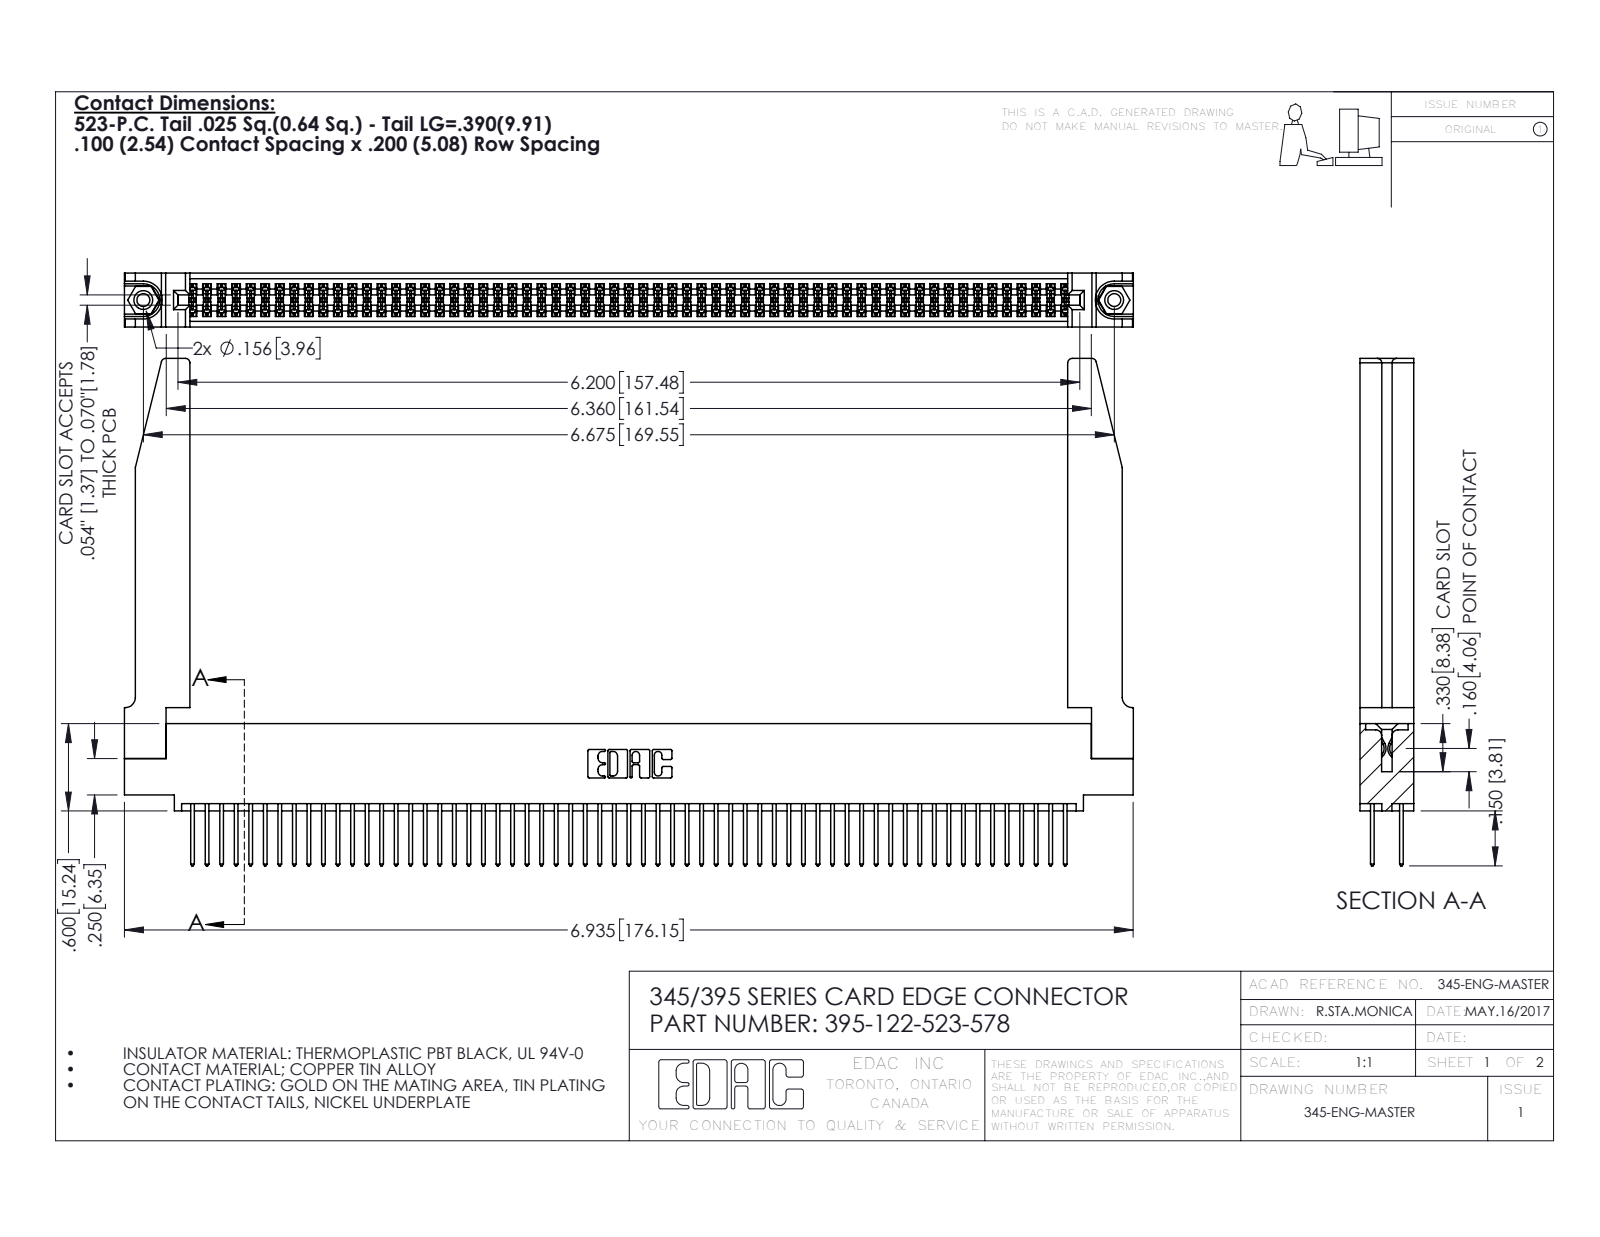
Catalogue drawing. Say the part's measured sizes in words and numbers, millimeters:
The part is named "345-220-078_345-220-078; 395-122-523-578; 345-292-001_345-293-123; 345 Part_0.110 Offset - 0.156 Dia-TH (+1 more)". Its 3-D file was written by "SolidWorks 2016 (CONFIG_CONTROL_DESIGN)". It is 127 solids with 6464 faces: 4252 planar, 2160 cylindrical and 52 other. Overall it measures 176.2 by 88.6 by 9.4 millimeters. Its volume is 25 240 cubic millimeters and its surface area 34 240 square millimeters. Round holes: 2 of diameter 2.3, 2 of diameter 3.2, 2 of diameter 4, 1 of diameter 1.6. Round bosses or shafts: 2 of diameter 3.9. Partial cylindrical surfaces (rounded edges, fillets, slot ends): 183 of radius 0.2, 122 of radius 0.3, 22 of radius 0.3, 8 of radius 0.8, 6 of radius 0.2, 6 of radius 0.8, 3 of radius 0.7, 2 of radius 0.4. The main face-to-face distances are 1.8, 7.6, 9.4, 2.5, 6.9, 0.6, 5.1, 5.7, 4.4, 3.8. The hole center spacings are 6.9, 163.6, 169.5.
